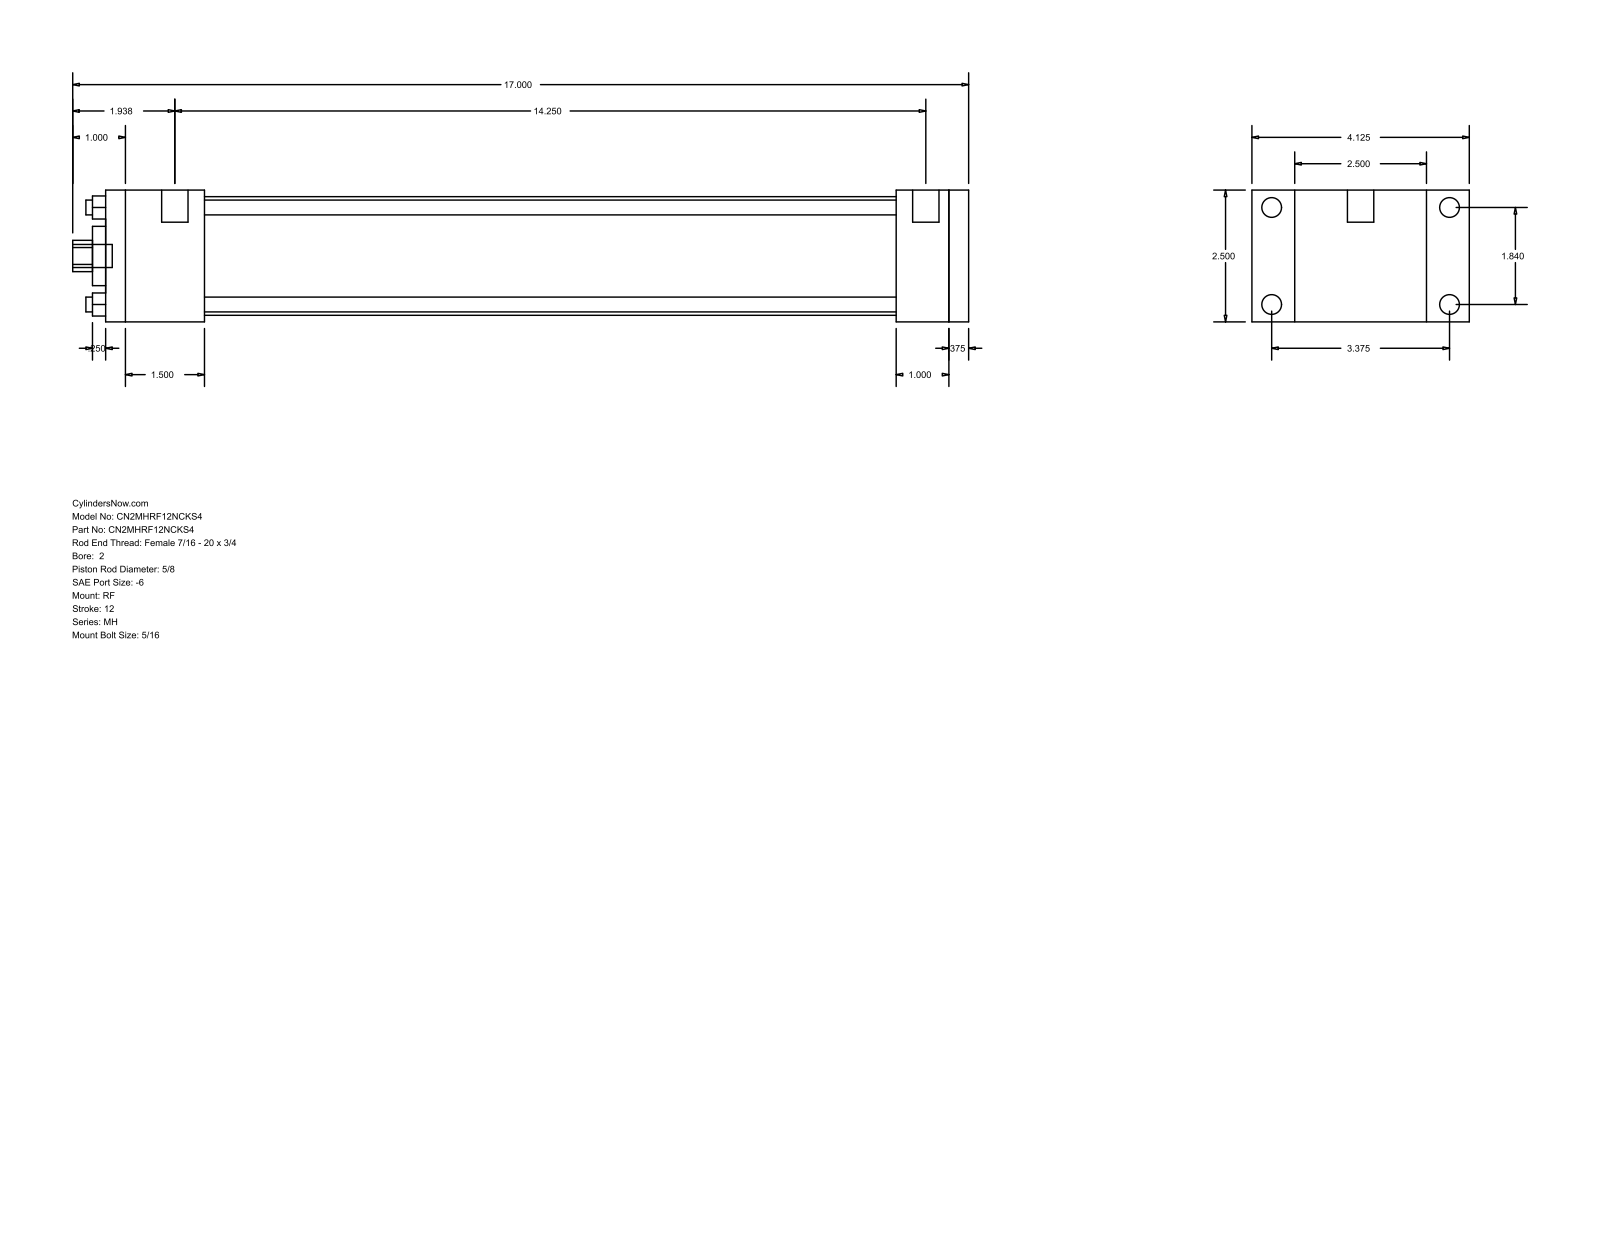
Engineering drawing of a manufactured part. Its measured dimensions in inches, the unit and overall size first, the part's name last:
Units: inches
Overall size (bounding box): 17 × 4.125 × 2.5
Round holes (diameter × count): ⌀0.281 ×4, ⌀0.625 ×1, ⌀1.125 ×1, ⌀2.25 ×1
Round bosses / shafts (diameter × count): ⌀0.375 ×4, ⌀0.219 ×4, ⌀0.5 ×2, ⌀0.437 ×1
Partial cylindrical surfaces — rounded edges, fillets, slot ends (radius × count): R0.297 ×1
Main face-to-face distances: 2.5, 16.375, 0.375, 16, 1.875, 15, 13.125, 14.125, 14.5, 1
Hole centre spacings: 1.301, 1.84, 2.602
Bodies: 0 solids, 92 faces (64 planar, 28 cylindrical, 0 other)
Part name (STEP PRODUCT): MH_RF__0200_0.625
STEP written by: GSSL Pune (CONFIG_CONTROL_DESIGN)
